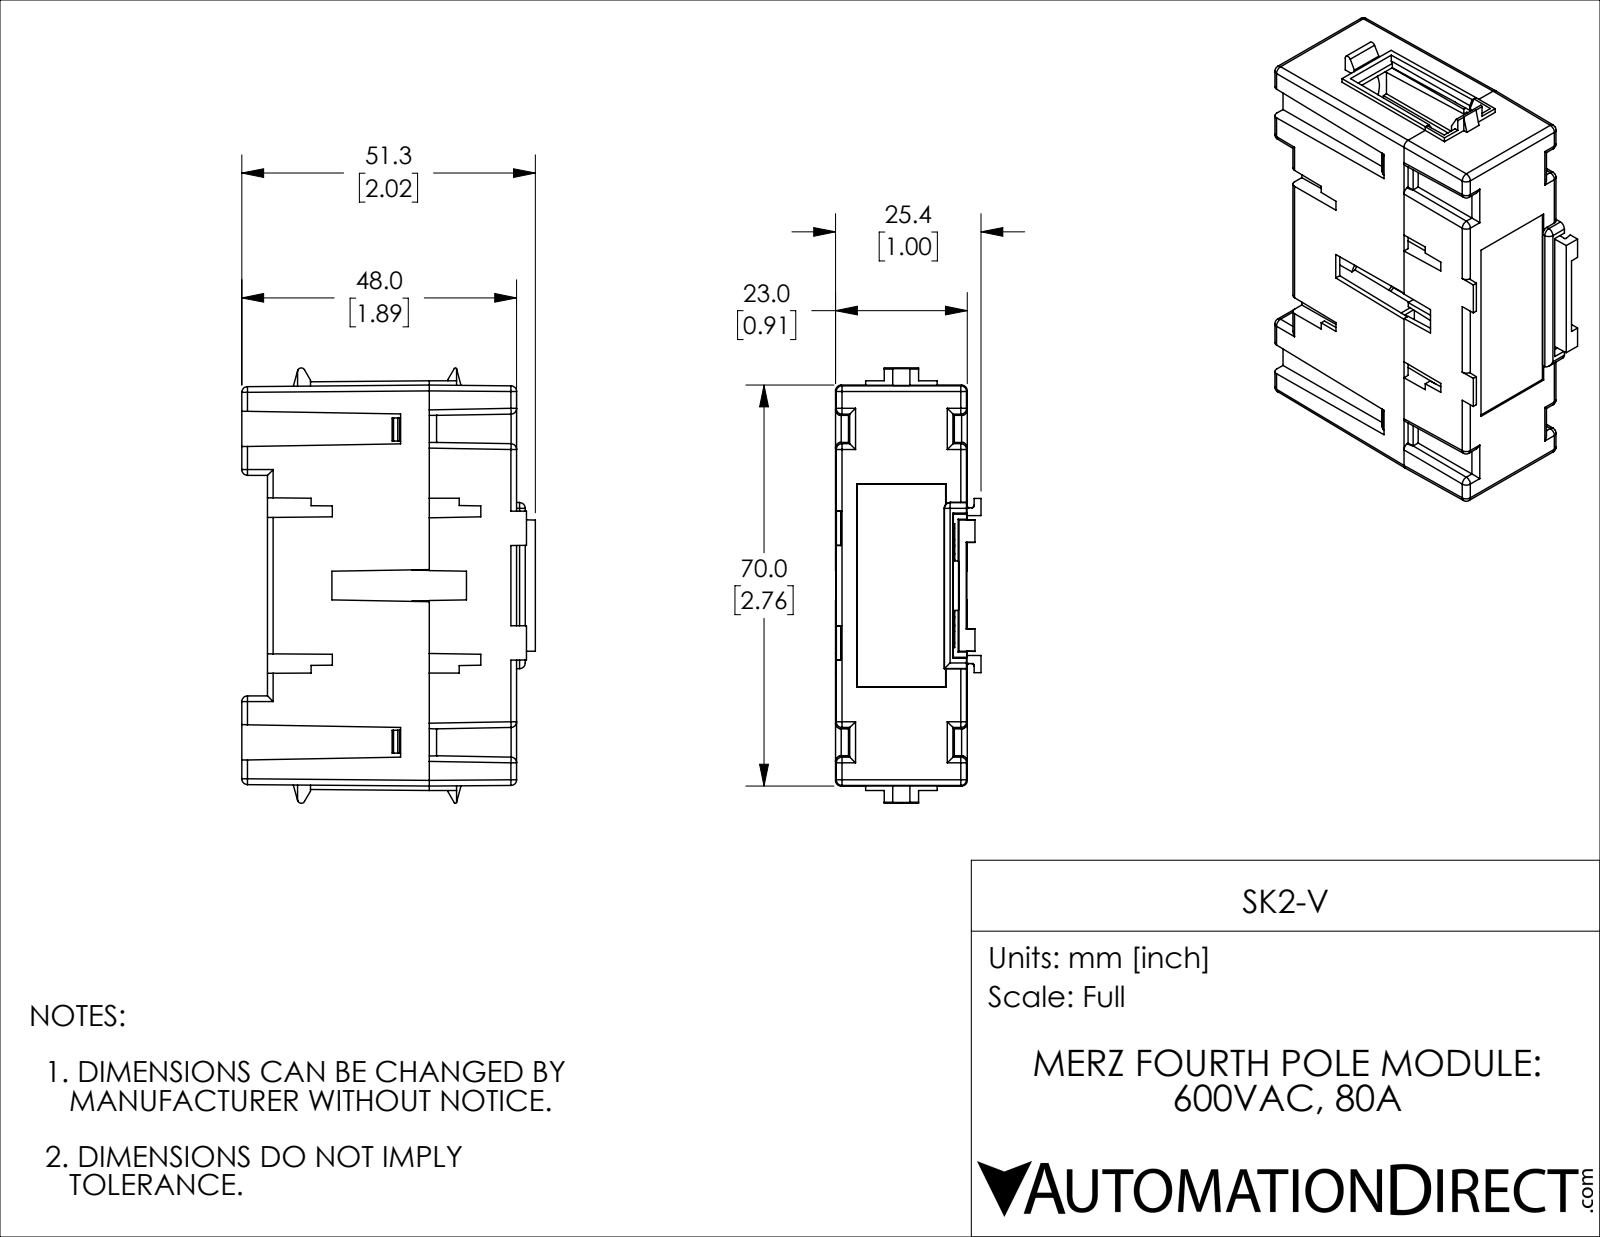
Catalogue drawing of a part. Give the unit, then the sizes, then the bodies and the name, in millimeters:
Units: millimetres
Overall size (bounding box): 76 × 51.3 × 25.4
Partial cylindrical surfaces — rounded edges, fillets, slot ends (radius × count): R1 ×42, R0.5 ×6, R0.3 ×4, R0.2 ×3, R0.6 ×2, R1.5 ×2
Main face-to-face distances: 1, 23, 4.5, 0.7, 42.2, 22, 2.5, 5.5, 53.8, 3
Volume: 25 880 mm³ · Surface area: 35 050 mm²
Bodies: 1 solid, 825 faces (656 planar, 85 cylindrical, 84 other)
Part name (STEP PRODUCT): SK2-V
STEP written by: SolidWorks 2019 (AUTOMOTIVE_DESIGN)
